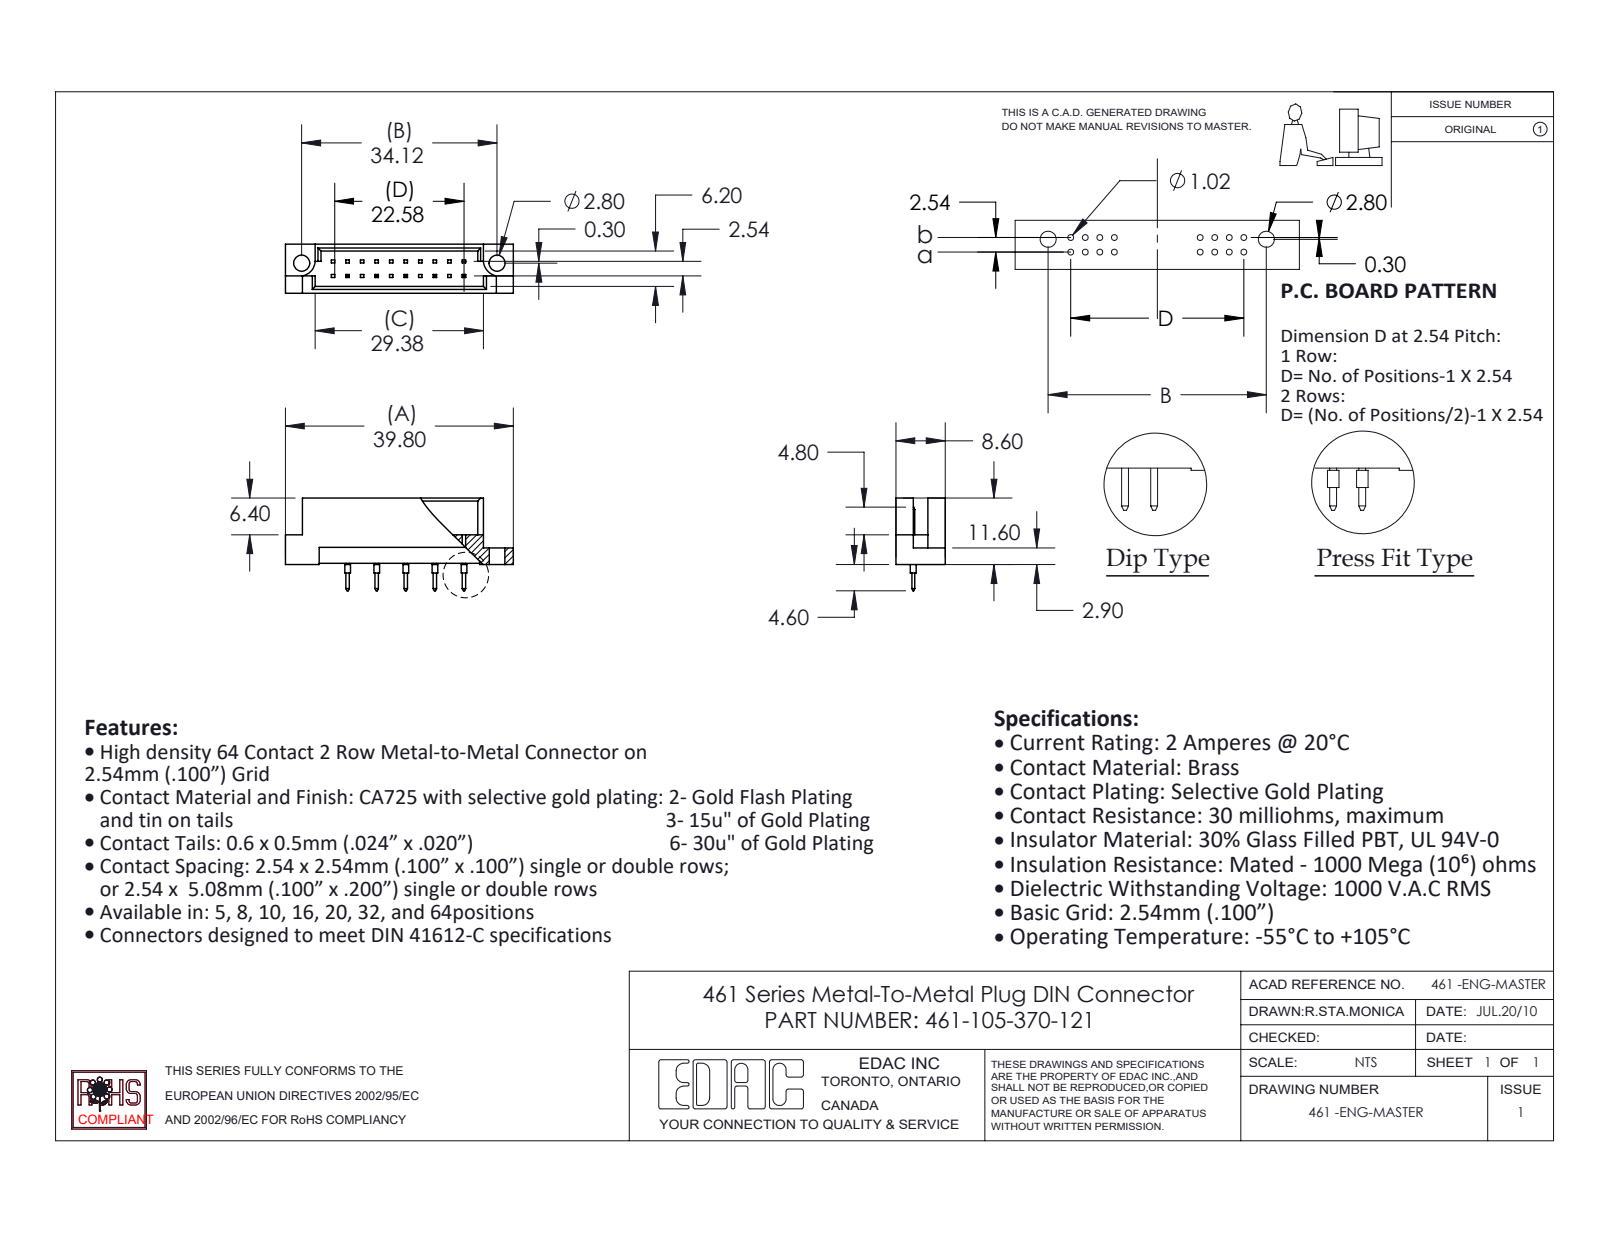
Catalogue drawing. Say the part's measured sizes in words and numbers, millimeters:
The part is named "461-290_70; 461-105-370-121; 461 Part_20". Its 3-D file was written by "SolidWorks 2020 (CONFIG_CONTROL_DESIGN)". It is 6 solids with 238 faces: 222 planar, 16 cylindrical and 0 other. Overall it measures 39.8 by 16.2 by 8.6 millimeters. Its volume is 1 930 cubic millimeters and its surface area 2 508 square millimeters. Round holes: 2 of diameter 2.8. Round bosses or shafts: 5 of diameter 1. Partial cylindrical surfaces (rounded edges, fillets, slot ends): 2 of radius 2.8. The main face-to-face distances are 1.2, 7.4, 8.6, 6.2, 5, 1.58, 3.28, 5.32, 2.08, 4.12. The hole center spacings are 34.12.
